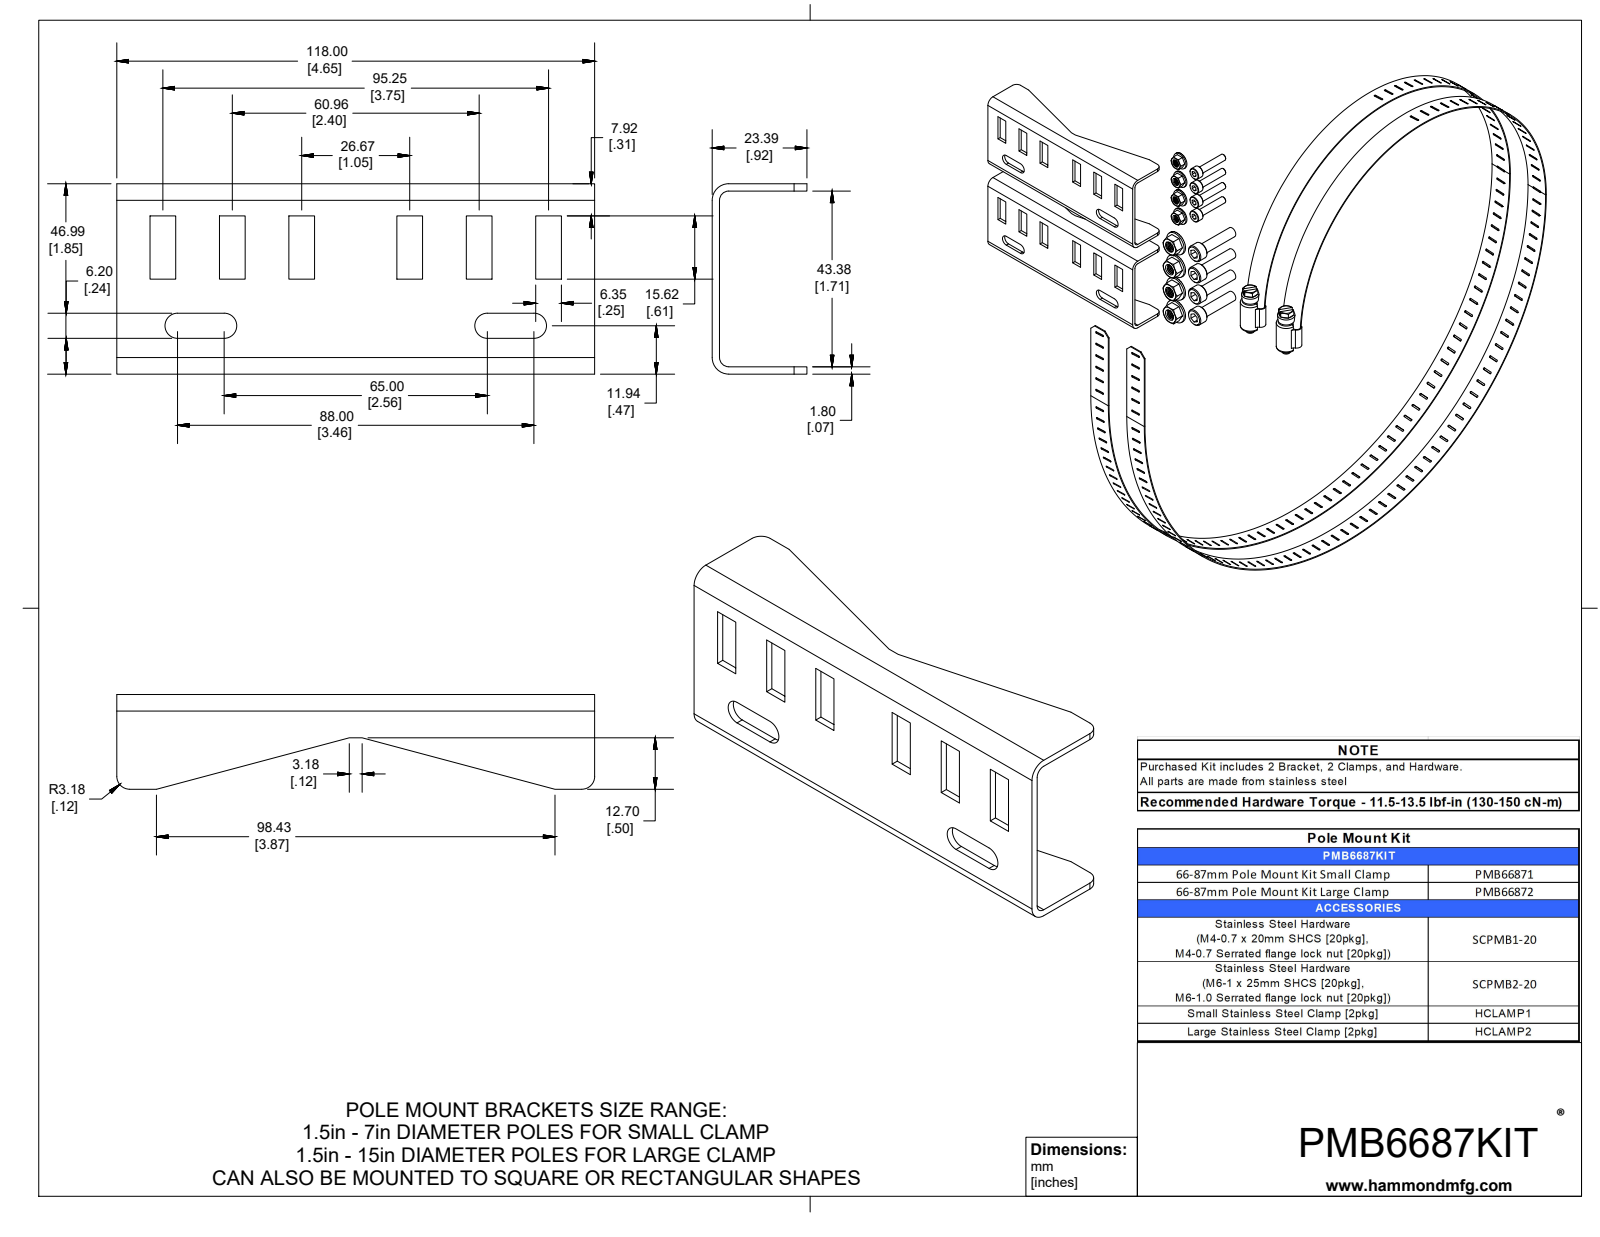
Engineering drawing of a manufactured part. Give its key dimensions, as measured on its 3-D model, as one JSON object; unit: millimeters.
{"part_name": "PMB6687KIT2", "step_written_by": "SolidWorks 2019 (CONFIG_CONTROL_DESIGN)", "units": "millimeters", "bodies": {"solids": 22, "faces": 1798, "planar": 1204, "cylindrical": 472, "other": 122}, "overall_size": [327.6, 264.1, 252.8], "volume_mm3": 55130, "surface_area_mm2": 101300, "round_holes": [[3.3, 4], [4.2, 4], [4.7, 4], [6, 4]], "round_bosses_or_shafts": [[10, 8], [14.2, 4], [10.6, 4], [7.4, 4], [6.9, 4], [6, 4], [4, 4], [8, 2]], "partial_cylinders_radius": [[0.5, 364], [3.2, 9], [3.1, 8], [2.3, 4], [2.5, 4], [3, 4], [4.1, 4], [5, 2]], "face_to_face_distances": [1.8, 57, 45.2, 58.8, 43.4, 102.2, 10, 1.8, 45.2, 47], "hole_center_spacings": [13, 16, 26.1, 32, 13.1, 16, 22.9, 35.7]}
